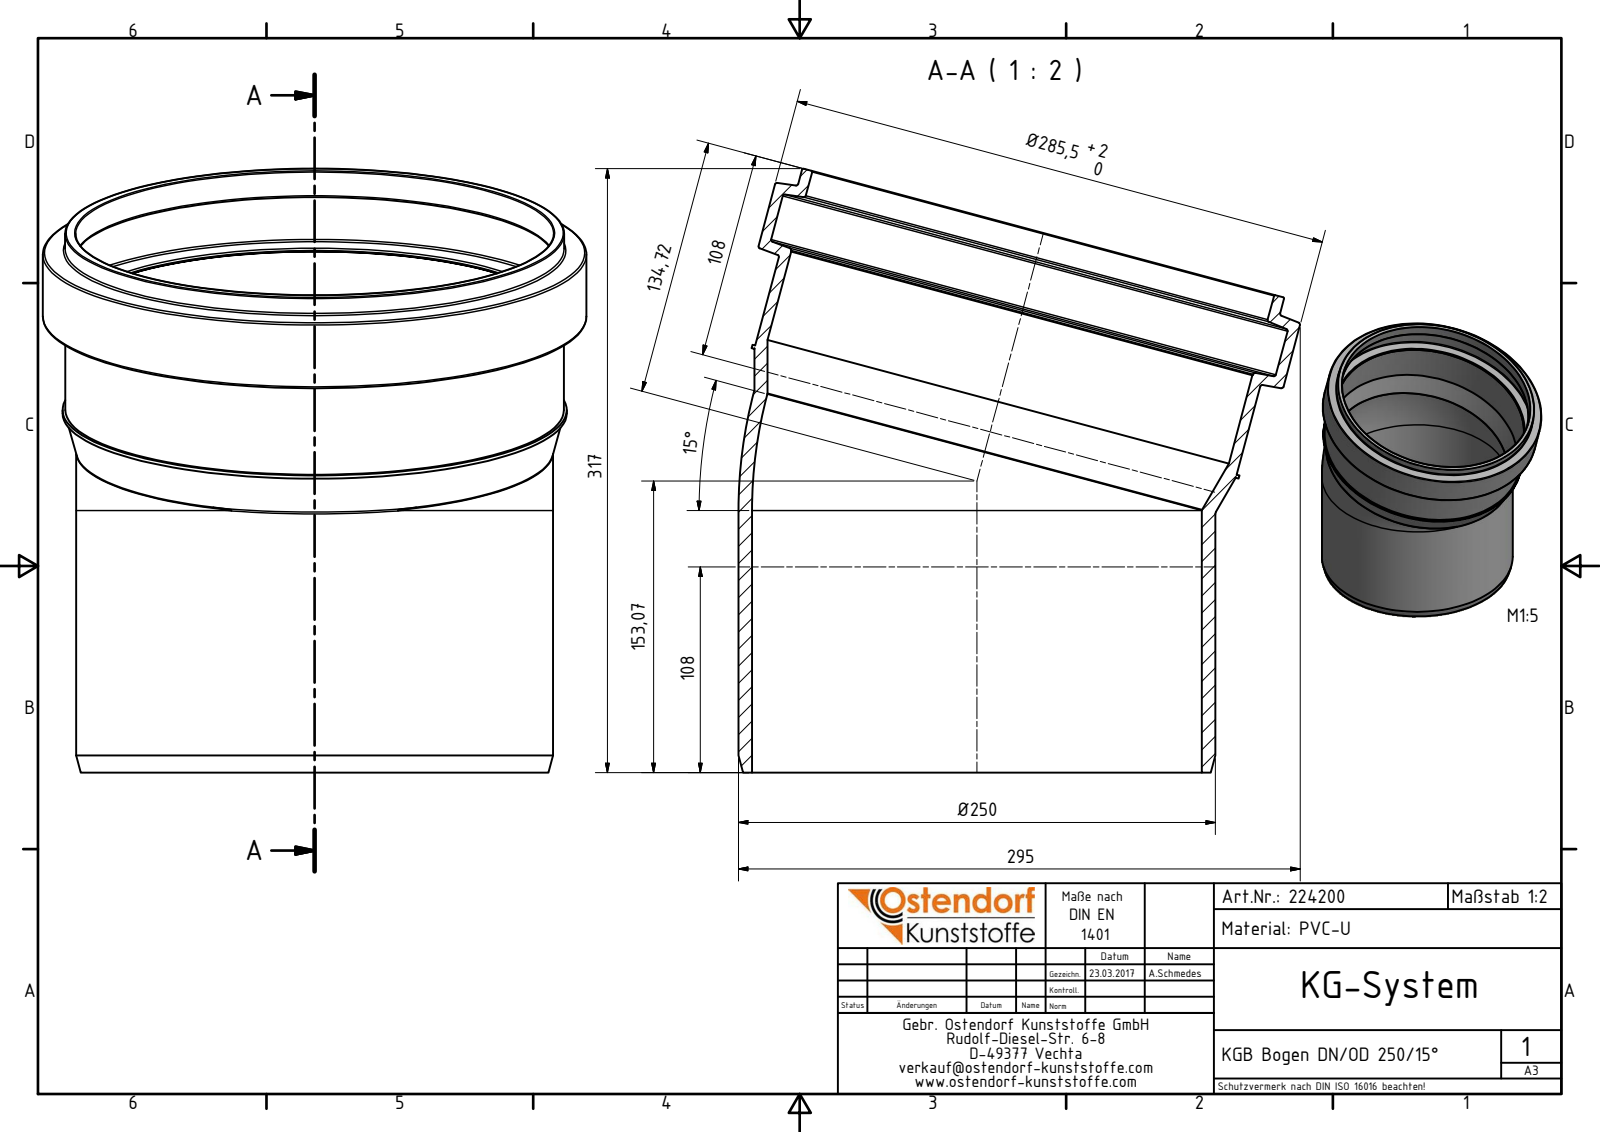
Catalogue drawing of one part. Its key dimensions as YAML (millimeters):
part_name: "224200 KGB Bogen DN_OD 250_15°"
step_written_by: "Autodesk Inventor 2016 (AUTOMOTIVE_DESIGN)"
units: millimeters
bodies: {solids: 1, faces: 40, planar: 5, cylindrical: 13, other: 22}
overall_size: [317, 295, 285.5]
volume: 1559000
surface_area: 499004
round_holes:
  - {diameter: 236.3, count: 2}
  - {diameter: 250.8, count: 1}
  - {diameter: 251.1, count: 1}
  - {diameter: 261.8, count: 1}
  - {diameter: 274.5, count: 1}
round_bosses_or_shafts:
  - {diameter: 250.5, count: 2}
  - {diameter: 285.5, count: 1}
  - {diameter: 264.8, count: 1}
  - {diameter: 262.1, count: 1}
  - {diameter: 261.8, count: 1}
face_to_face_distances: [98.01, 1.8, 96.21, 54.37, 52.57, 43.64]
